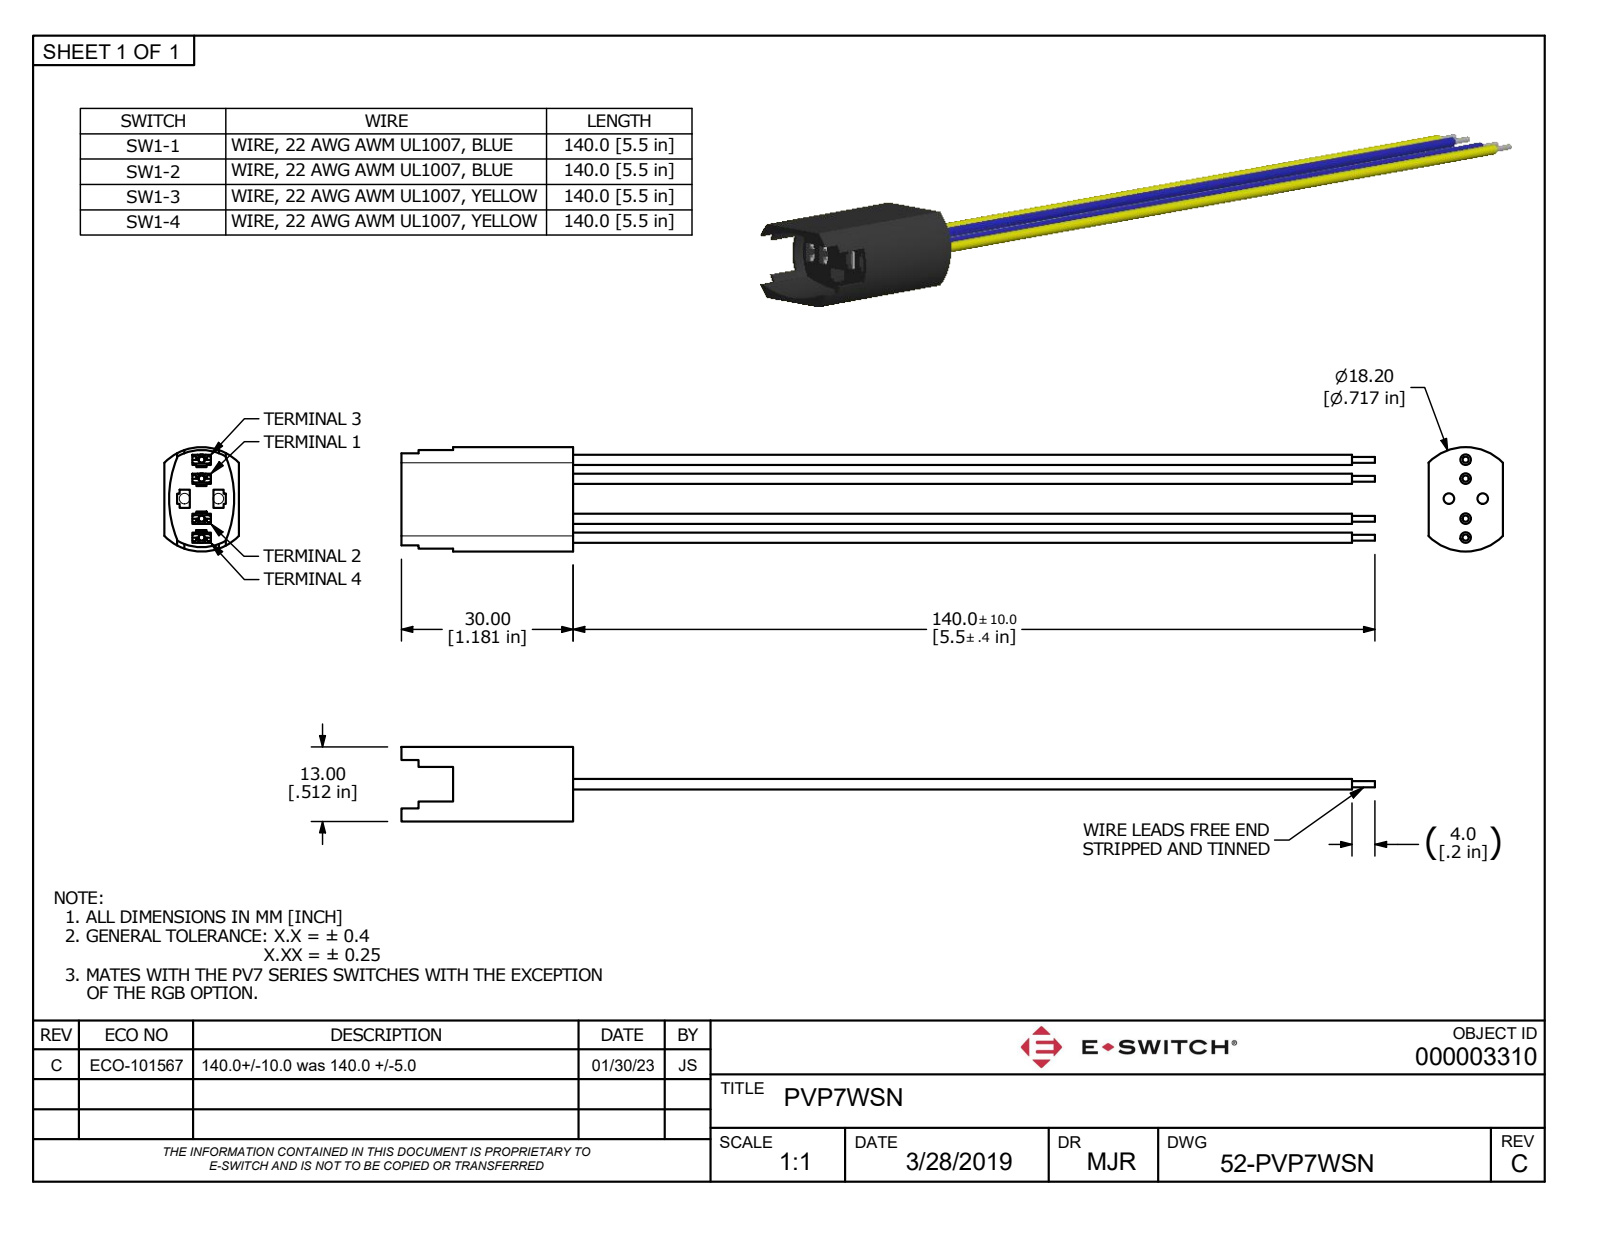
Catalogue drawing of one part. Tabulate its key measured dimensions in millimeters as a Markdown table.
| quantity | value |
| --- | --- |
| part name | PVP7WSN |
| STEP written by | Autodesk Inventor 2018 (AP242_MANAGED_MODEL_BASED_3D_ENGINEERING_MIM_LF) |
| units | millimeters |
| bodies | 1 solid, 262 faces (178 planar, 60 cylindrical, 24 other) |
| overall size | 170 × 18.2 × 13 |
| volume | 5 424 mm³ |
| surface area | 6 996 mm² |
| round holes (diameter × count) | 1.8 × 2 |
| round bosses / shafts (diameter × count) | 1.8 × 4 |
| partial cylindrical surfaces (radius × count) | 0.25 × 24, 0.5 × 8, 0.52 × 4, 18.8 × 2, 8.47 × 1, 9.1 × 1 |
| main face-to-face distances | 13, 8.1, 3.3, 2.2, 4.9, 3.2, 1.8, 2.25, 2.65, 18.9 |
| hole center spacings | 5.9 |
